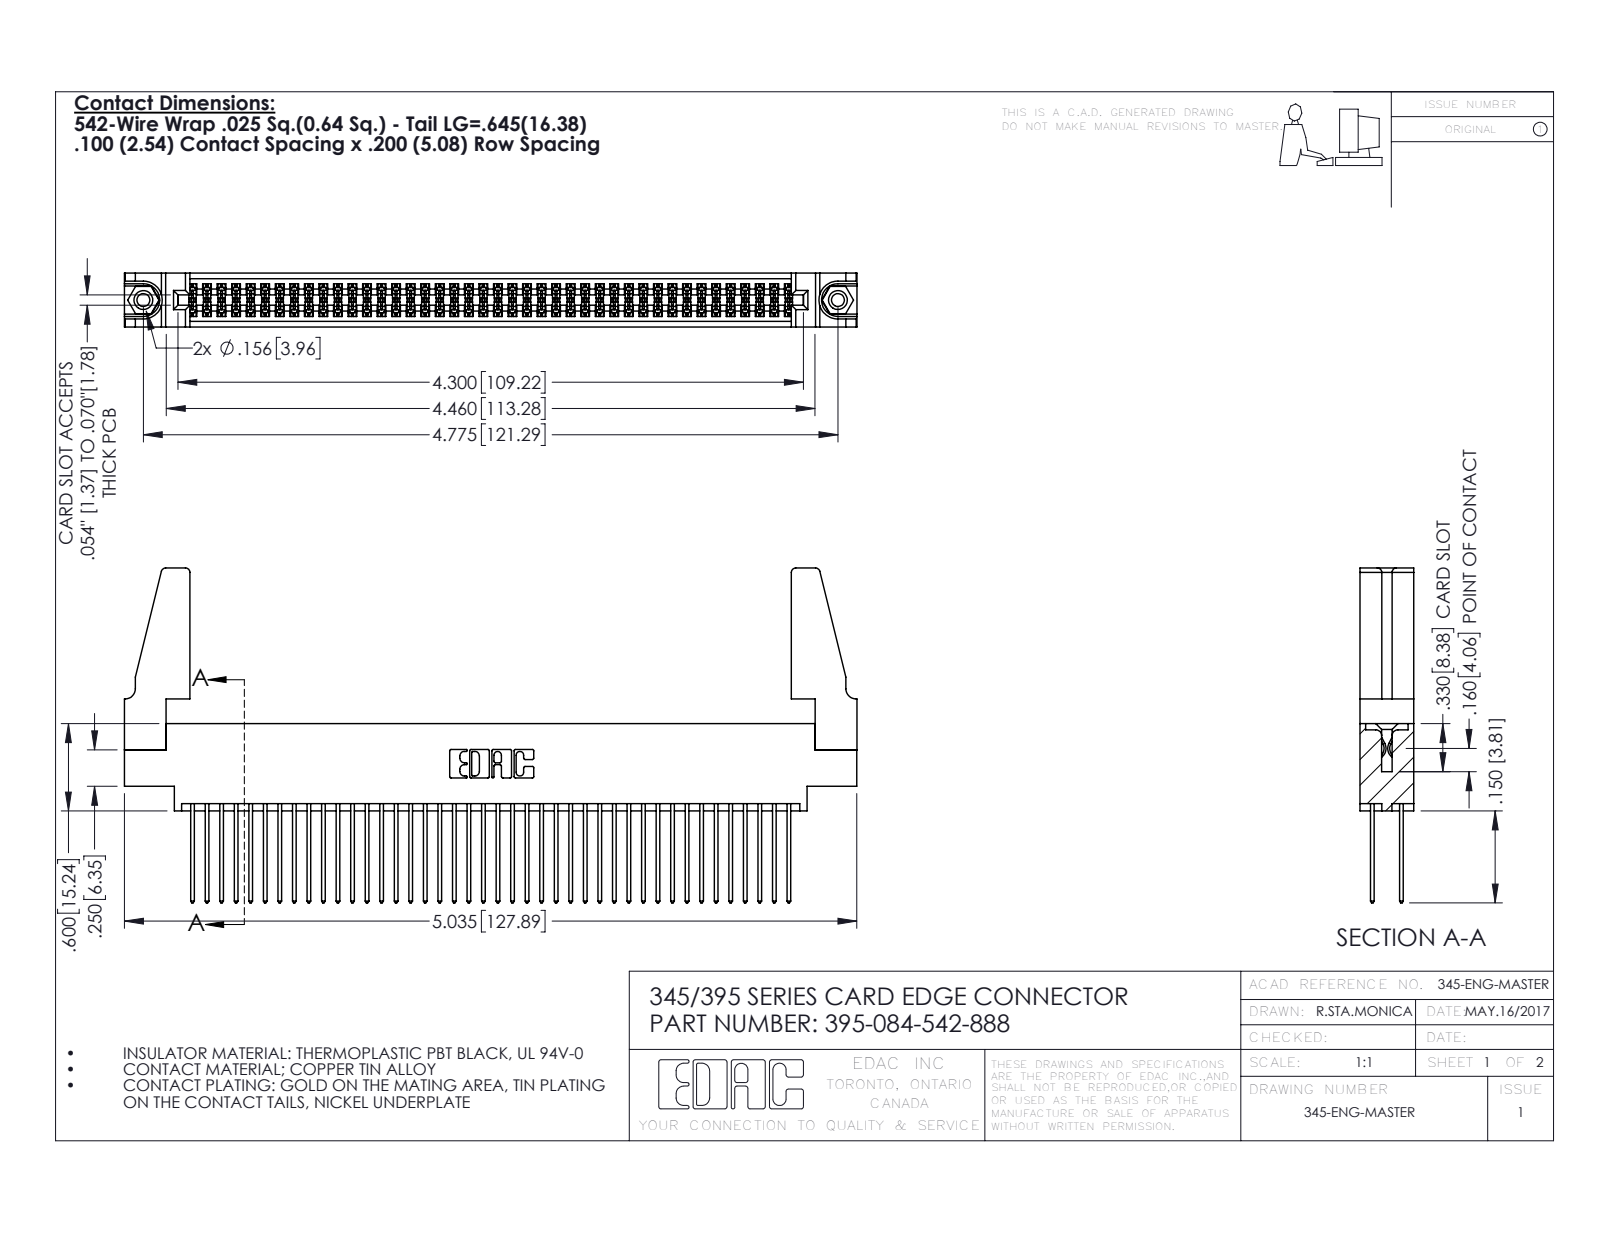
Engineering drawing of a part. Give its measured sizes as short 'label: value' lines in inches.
name: 395-084-542-888; 345 Part_0.170 Offset - 0.156 Dia-TH; 345-292-001_345-293-142; 345-250-001_345-250-001-102 (+1 more)
written by: SolidWorks 2016 (CONFIG_CONTROL_DESIGN)
unit: in
bodies: 89 solids, 4454 faces (2928 planar, 1510 cylindrical, 16 other)
size: 5.036 × 2.302 × 0.37
volume: 0.974 in³; area: 37 in²
holes: 2× ⌀0.089, 2× ⌀0.125, 2× ⌀0.156, 1× ⌀0.064
bosses: 2× ⌀0.155
rounds: 126× R0.006, 84× R0.01, 22× R0.01, 8× R0.03, 6× R0.007, 6× R0.031, 3× R0.026, 2× R0.014
face distances: 0.072, 0.298, 0.2, 0.37, 0.098, 0.272, 0.025, 0.225, 0.175, 0.149
hole spacings: 0.27, 4.539, 4.775
